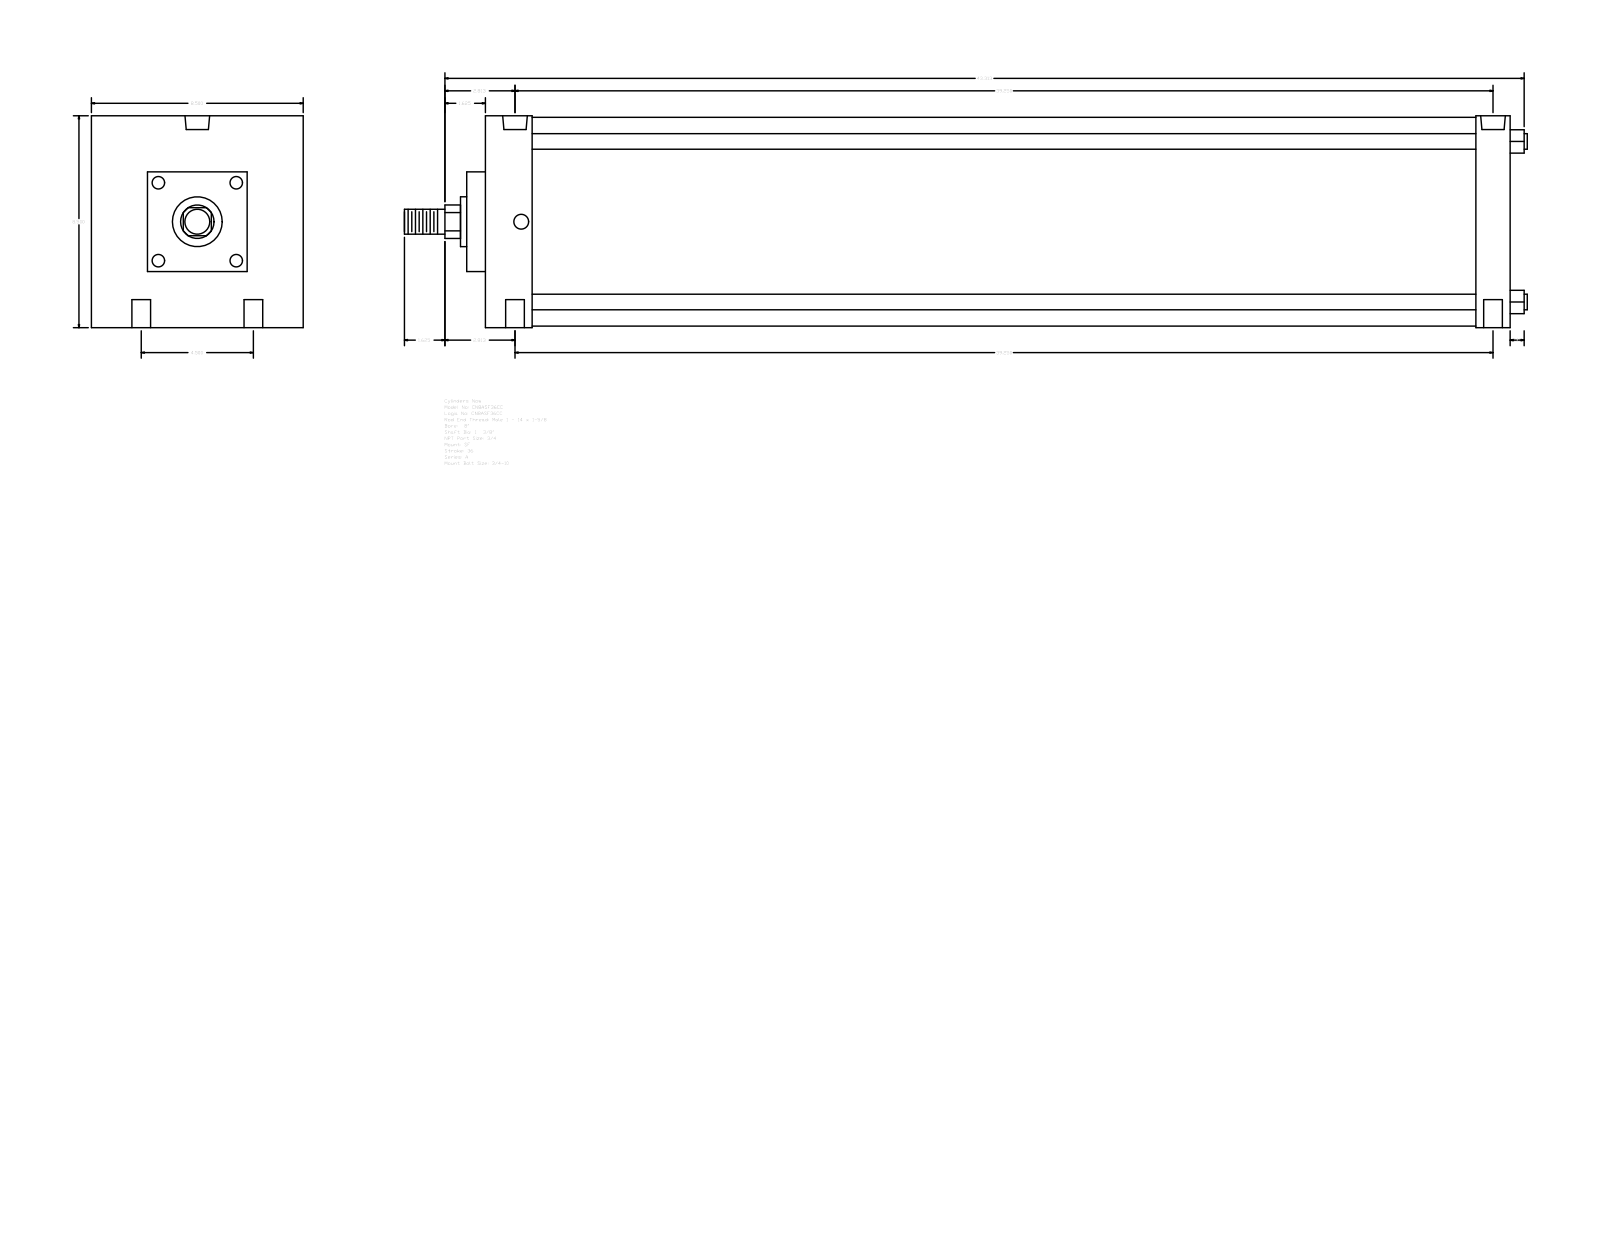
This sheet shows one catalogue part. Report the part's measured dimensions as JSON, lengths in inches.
{"part_name": "A_SF__0800_1.375", "step_written_by": "GSSL Pune (CONFIG_CONTROL_DESIGN)", "units": "inches", "bodies": {"solids": 0, "faces": 93, "planar": 67, "cylindrical": 26, "other": 0}, "overall_size": [45.063, 8.5, 8.5], "round_holes": [[0.75, 4], [0.594, 2], [0.989, 2]], "round_bosses_or_shafts": [[0.625, 4], [8.375, 1], [2, 1], [1.375, 1], [1, 1]], "partial_cylinders_radius": [[0.672, 1]], "face_to_face_distances": [41.125, 8.5, 1.875, 39.75, 37.875, 39.25, 1.375, 0.75, 2.625, 40.5], "hole_center_spacings": [2.25, 39.315, 39.25, 4.5, 39.507, 38.75]}
